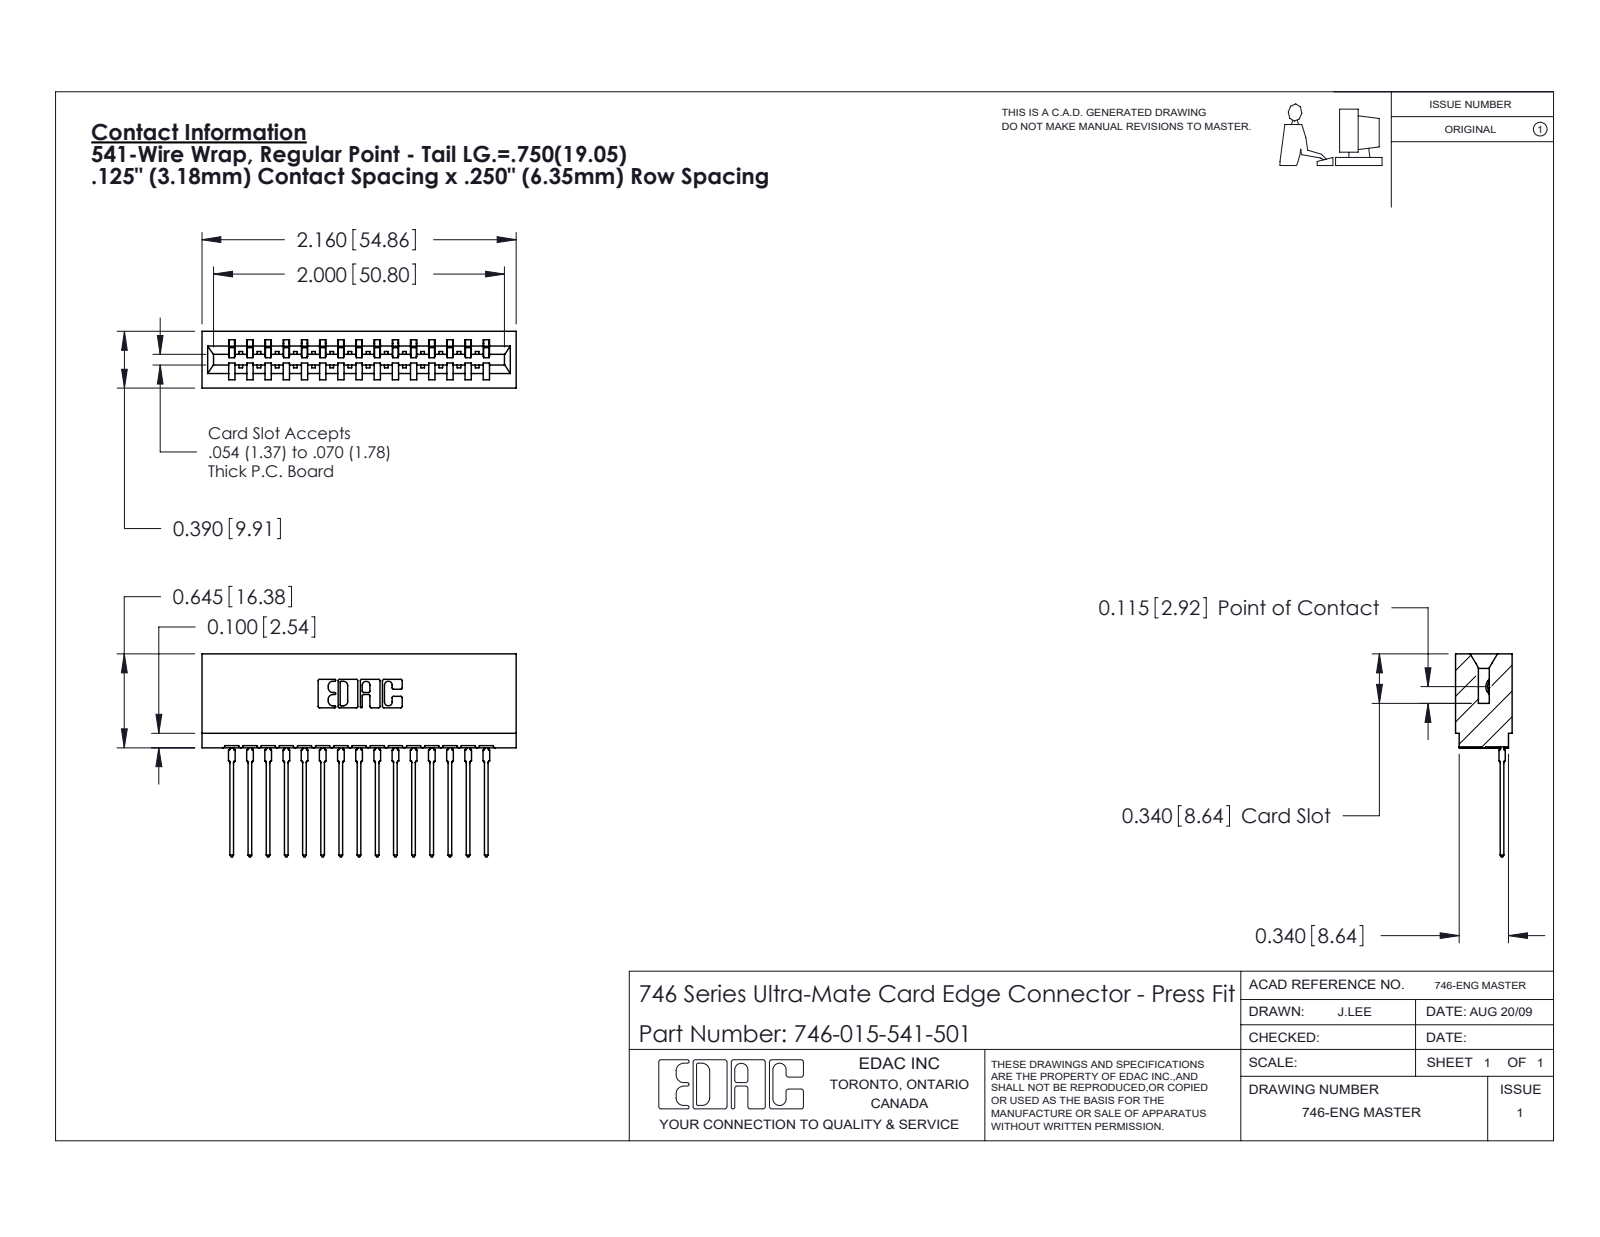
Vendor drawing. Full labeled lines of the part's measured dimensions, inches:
Part name (STEP PRODUCT): 746-292-001_541; 746-015-541-501; 746 Part_.340 Slot Depth - 01
STEP written by: SolidWorks 2020 (CONFIG_CONTROL_DESIGN)
Units: inches
Bodies: 16 solids, 1717 faces (1000 planar, 327 cylindrical, 390 other)
Overall size (bounding box): 2.16 × 1.394 × 0.39
Volume: 0.39 in³ · Surface area: 13.3 in²
Partial cylindrical surfaces — rounded edges, fillets, slot ends (radius × count): R0.021 ×30, R0.01 ×22, R0.015 ×16, R0.007 ×6, R0.031 ×6, R0.005 ×4, R0.011 ×4, R0.026 ×3
Main face-to-face distances: 0.25, 0.057, 0.333, 0.5, 0.39, 0.125, 0.042, 0.292, 0.125, 0.025
